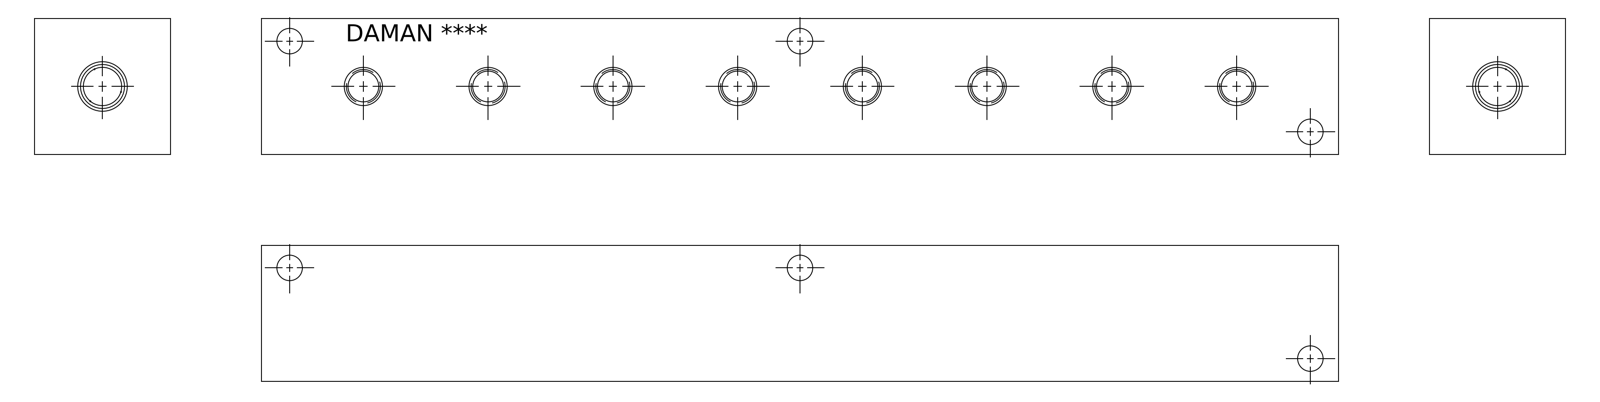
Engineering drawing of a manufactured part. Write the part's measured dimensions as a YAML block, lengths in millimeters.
part_name: "Part_+H0000802P_3D"
step_written_by: "Autodesk Inventor 2020 (AUTOMOTIVE_DESIGN)"
units: millimeters
bodies: {solids: 1, faces: 363, planar: 215, cylindrical: 32, other: 116}
overall_size: [301.62, 38.1, 38.1]
volume: 419980
surface_area: 56130
round_holes:
  - {diameter: 8.43, count: 8}
  - {diameter: 10.33, count: 8}
  - {diameter: 7.14, count: 6}
  - {diameter: 10.72, count: 1}
  - {diameter: 13.87, count: 1}
face_to_face_distances: [38.1, 301.62, 30.23, 7.87, 11.4, 290.22, 38.06, 7.83, 278.82, 3.62]
hole_center_spacings: [34.93, 69.85, 34.92, 104.78, 139.7, 104.77, 142.91, 145.08]
